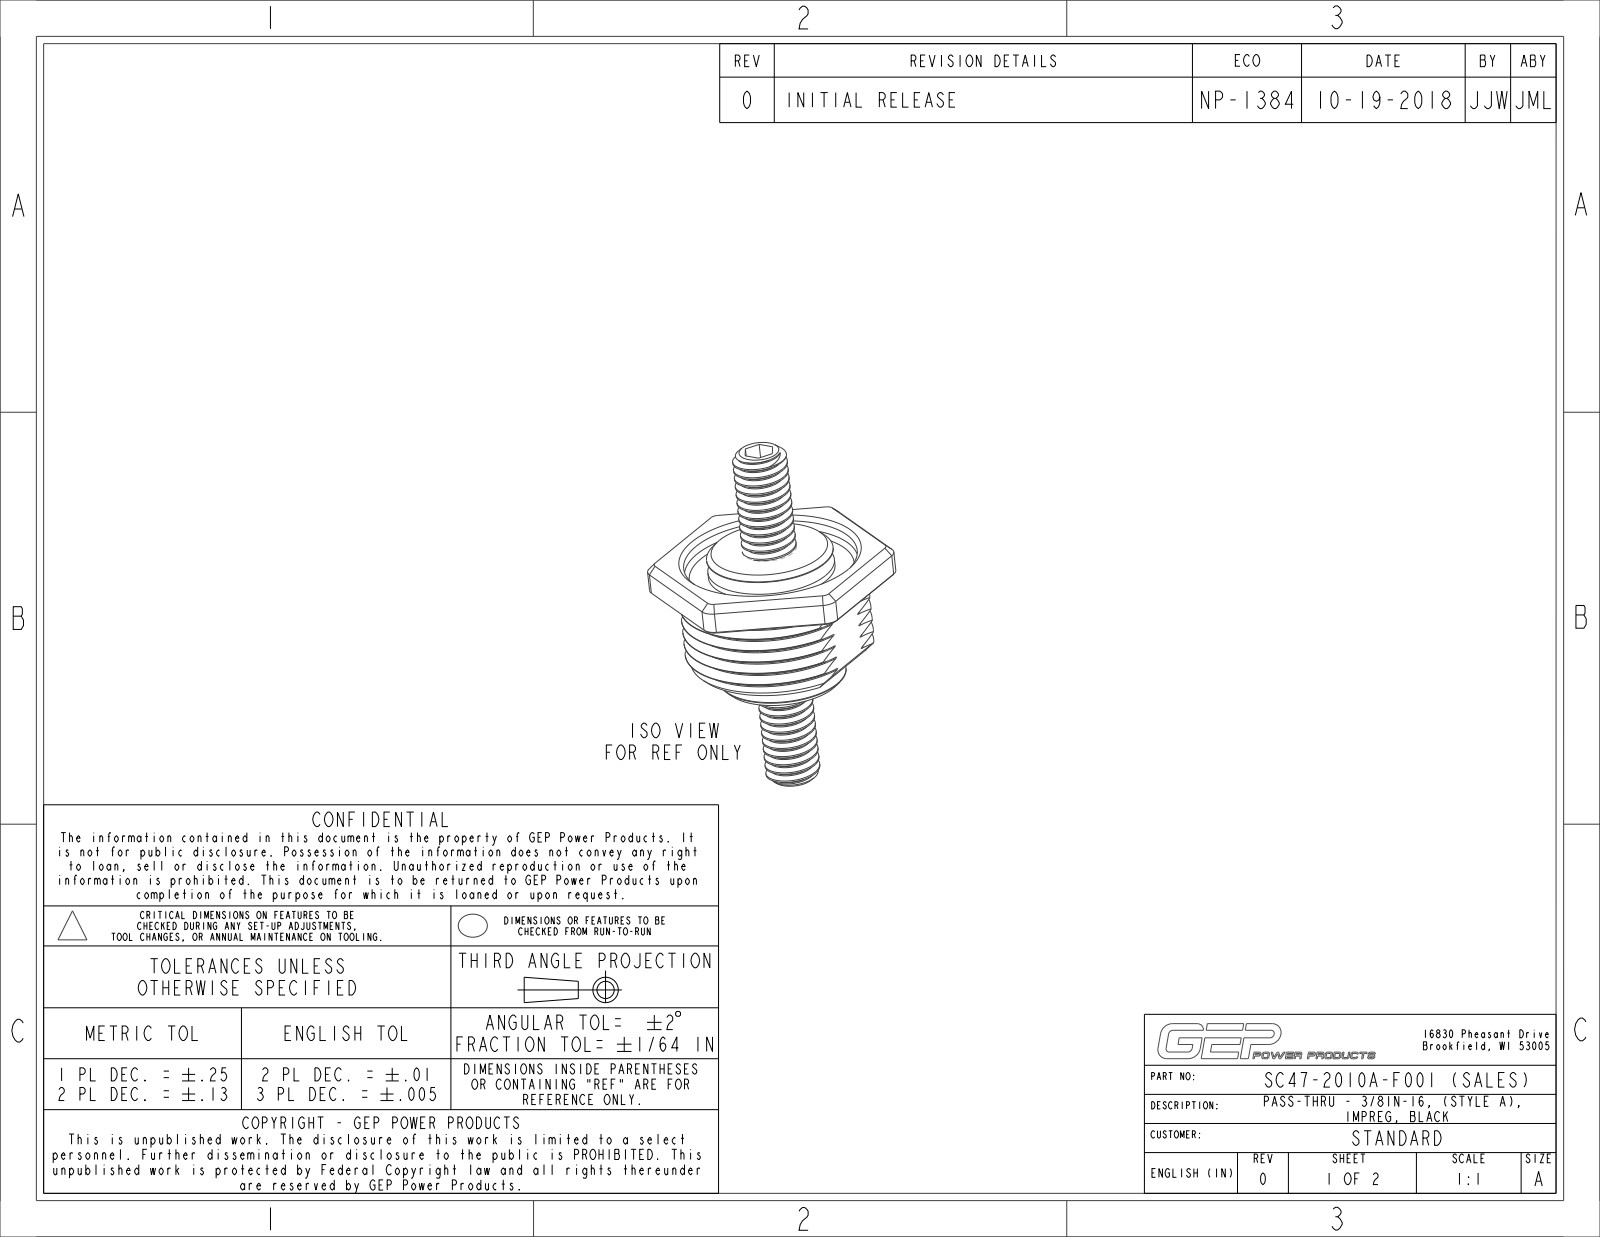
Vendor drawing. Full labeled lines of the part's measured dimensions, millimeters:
Part name (STEP PRODUCT): SC47-2010A-F008_NCF_SW0001
STEP written by: CREO PARAMETRIC BY PTC INC, 2017110 (CONFIG_CONTROL_DESIGN)
Units: millimetres
Bodies: 1 solid, 278 faces (47 planar, 93 cylindrical, 138 other)
Overall size (bounding box): 63.5 × 43.21 × 38.1
Volume: 19 893 mm³ · Surface area: 9 134 mm²
Round holes (diameter × count): ⌀7.94 ×1, ⌀30.48 ×1
Round bosses / shafts (diameter × count): ⌀22.23 ×1, ⌀9.53 ×1
Partial cylindrical surfaces — rounded edges, fillets, slot ends (radius × count): R2.54 ×6, R0.76 ×2, R16.57 ×1
Main face-to-face distances: 4.32, 21.08, 6.35, 1.27, 19.05, 5.08, 25.4, 14.73, 19.81, 16.76
